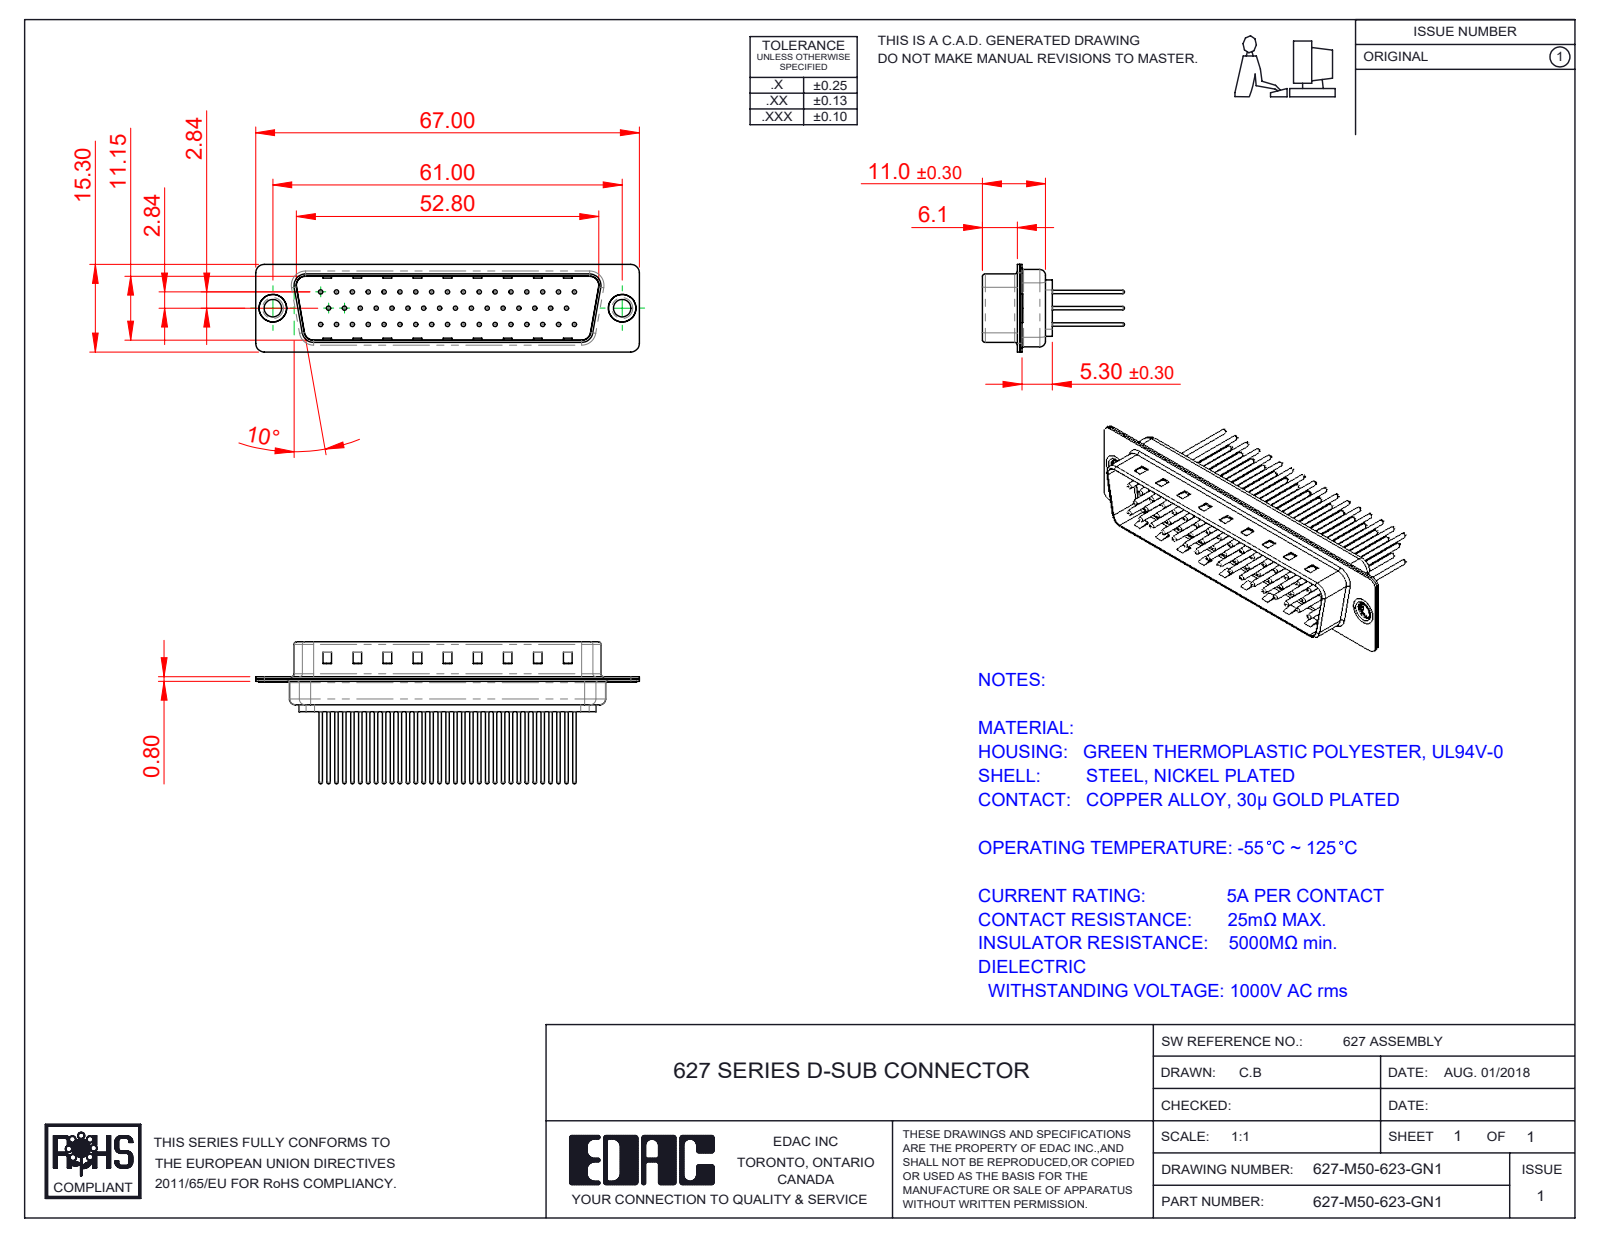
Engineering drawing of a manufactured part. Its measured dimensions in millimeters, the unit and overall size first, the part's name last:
Units: millimetres
Overall size (bounding box): 67 × 24.77 × 15.3
Round holes (diameter × count): ⌀0.75 ×50, ⌀1.6 ×50, ⌀2 ×50, ⌀3.05 ×2, ⌀4 ×2, ⌀4.8 ×2
Round bosses / shafts (diameter × count): ⌀1.5 ×50, ⌀0.6 ×50, ⌀5 ×2, ⌀4.9 ×2, ⌀3.55 ×2
Partial cylindrical surfaces — rounded edges, fillets, slot ends (radius × count): R1.5 ×16, R2 ×12, R0.5 ×8, R1.6 ×8, R0.25 ×4, R0.6 ×4, R0.65 ×4, R0.9 ×4
Main face-to-face distances: 0.4, 11.55, 5.7, 6.1, 0.78, 0.77, 12.33, 12.32, 13.1, 5.3
Hole centre spacings: 3.16, 2.77, 5.54, 8.31, 11.08, 13.85, 16.62, 5.03
Volume: 4 544 mm³ · Surface area: 11 201 mm²
Bodies: 55 solids, 2236 faces (553 planar, 825 cylindrical, 858 other)
Part name (STEP PRODUCT): 627-M50-623-GN1; 627M Shell Rear_50 Contacts; 627M Housing_50 Contacts; 627M Thru Hole Rivet (+4 more)
STEP written by: SolidWorks 2020 (CONFIG_CONTROL_DESIGN)
